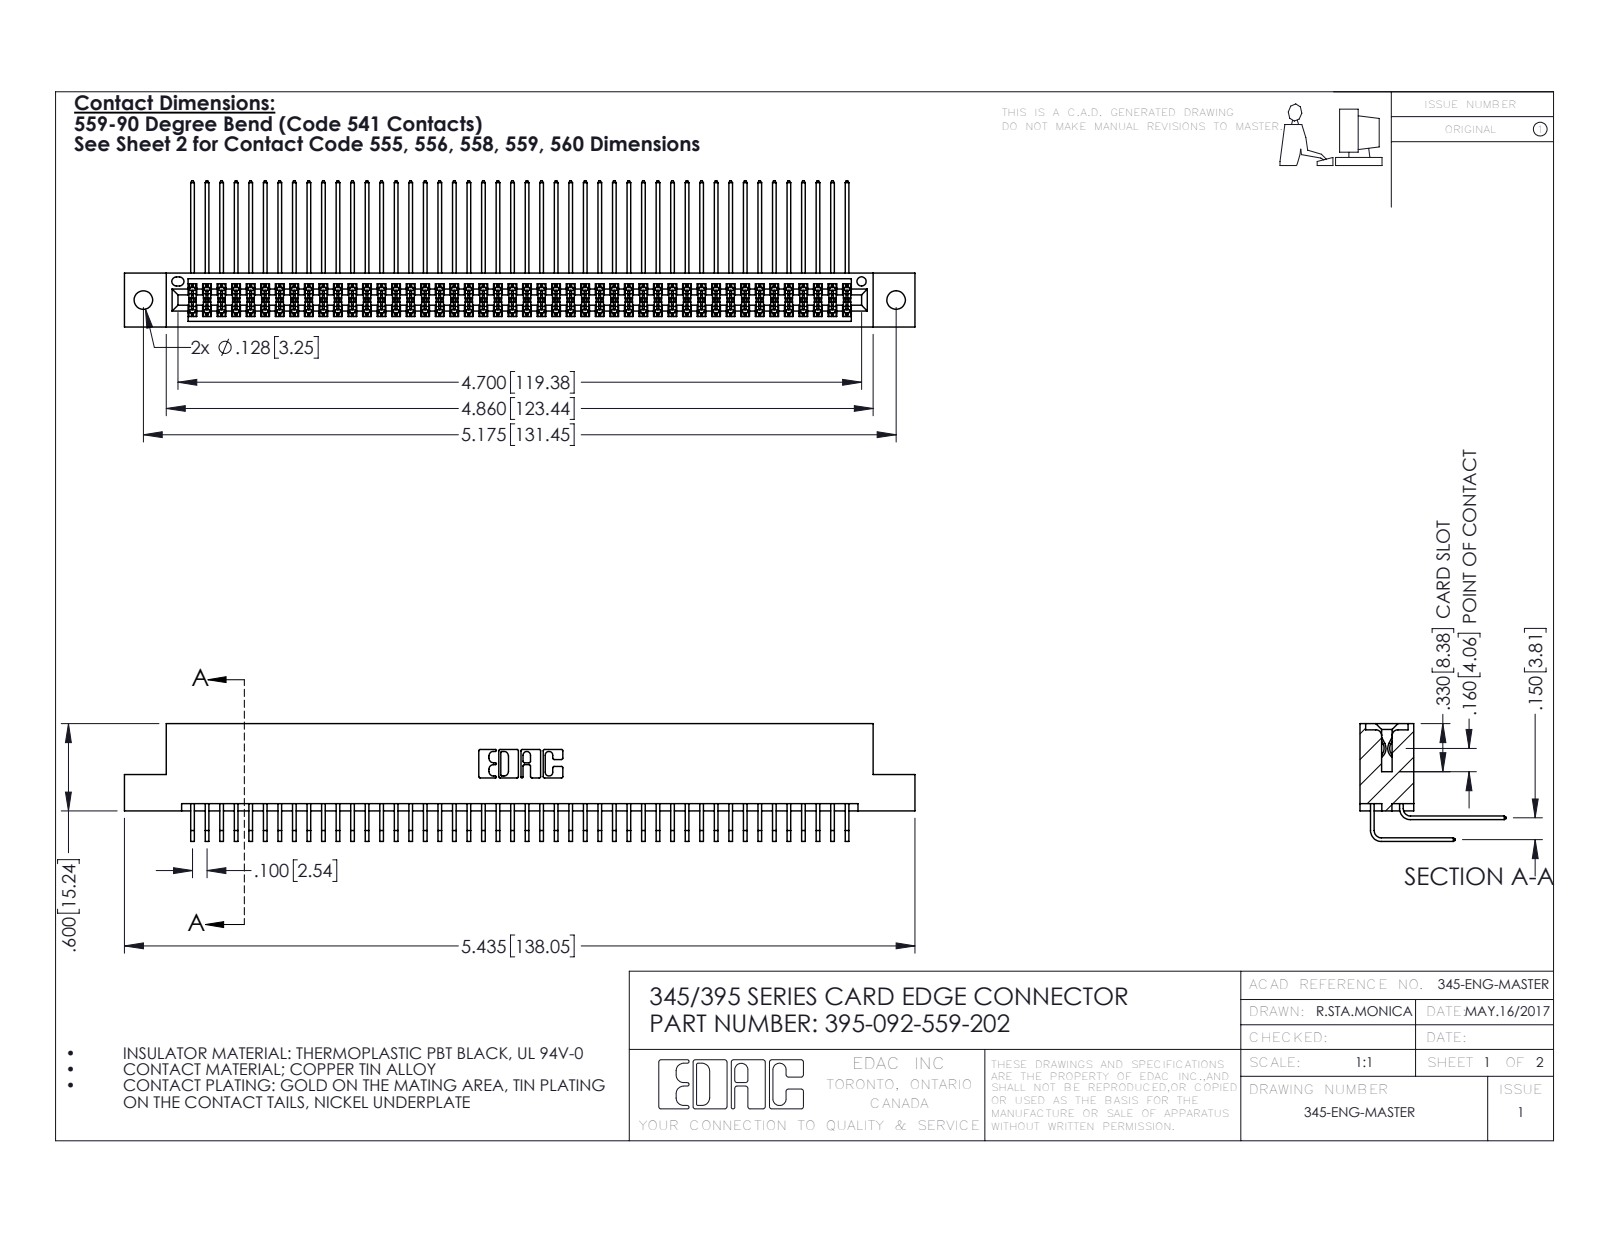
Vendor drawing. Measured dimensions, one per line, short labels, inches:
name: 345 Part_Flush Mounting Lugs - 0.128 Dia; 395-092-559-202; 345-292-001_559 Tail - 2; 345-292-001_558 559 Tail - 1
written by: SolidWorks 2016 (CONFIG_CONTROL_DESIGN)
unit: in
bodies: 93 solids, 4910 faces (3300 planar, 1610 cylindrical, 0 other)
size: 5.435 × 1.005 × 0.809
volume: 0.851 in³; area: 35.51 in²
holes: 2× ⌀0.128, 1× ⌀0.064
rounds: 138× R0.006, 22× R0.01, 6× R0.007, 6× R0.031, 3× R0.026, 2× R0.014, 2× R0.019, 2× R0.022
face distances: 0.072, 0.298, 0.2, 0.37, 0.098, 0.272, 0.025, 0.225, 0.175, 0.15
hole spacings: 0.27, 4.939, 5.175
